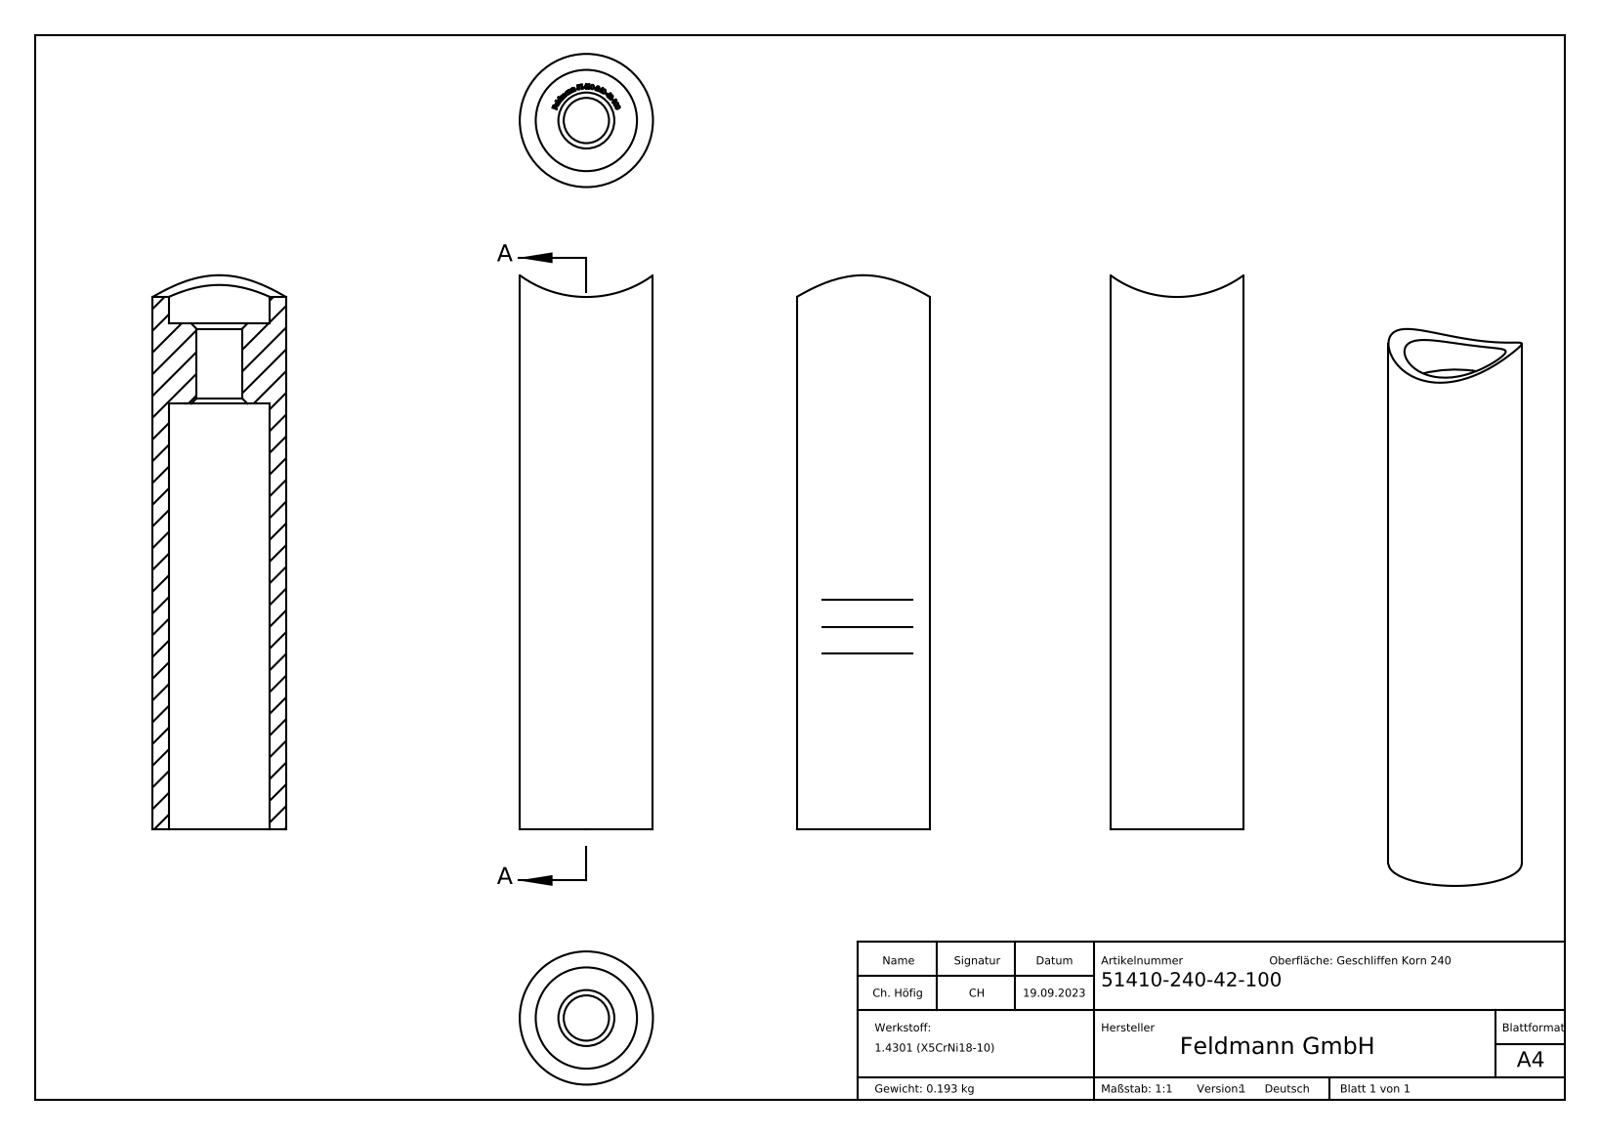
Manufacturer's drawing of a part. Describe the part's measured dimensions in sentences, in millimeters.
The part is named "51410-240-42-100". Its 3-D file was written by "SolidWorks 2018 (CONFIG_CONTROL_DESIGN)". It is 1 solid with 289 faces: 178 planar, 5 cylindrical and 106 other. Overall it measures 104.08 by 25 by 25 millimeters. Its volume is 24 425 cubic millimeters and its surface area 14 414 square millimeters. Round holes: 1 of diameter 8.5, 1 of diameter 19. Round bosses or shafts: 1 of diameter 25. Partial cylindrical surfaces (rounded edges, fillets, slot ends): 1 of radius 21.2. The main face-to-face distances are 95, 80, 15, 80.1, 14.9, 0.4, 0.44, 0.33, 0.47, 0.8.
